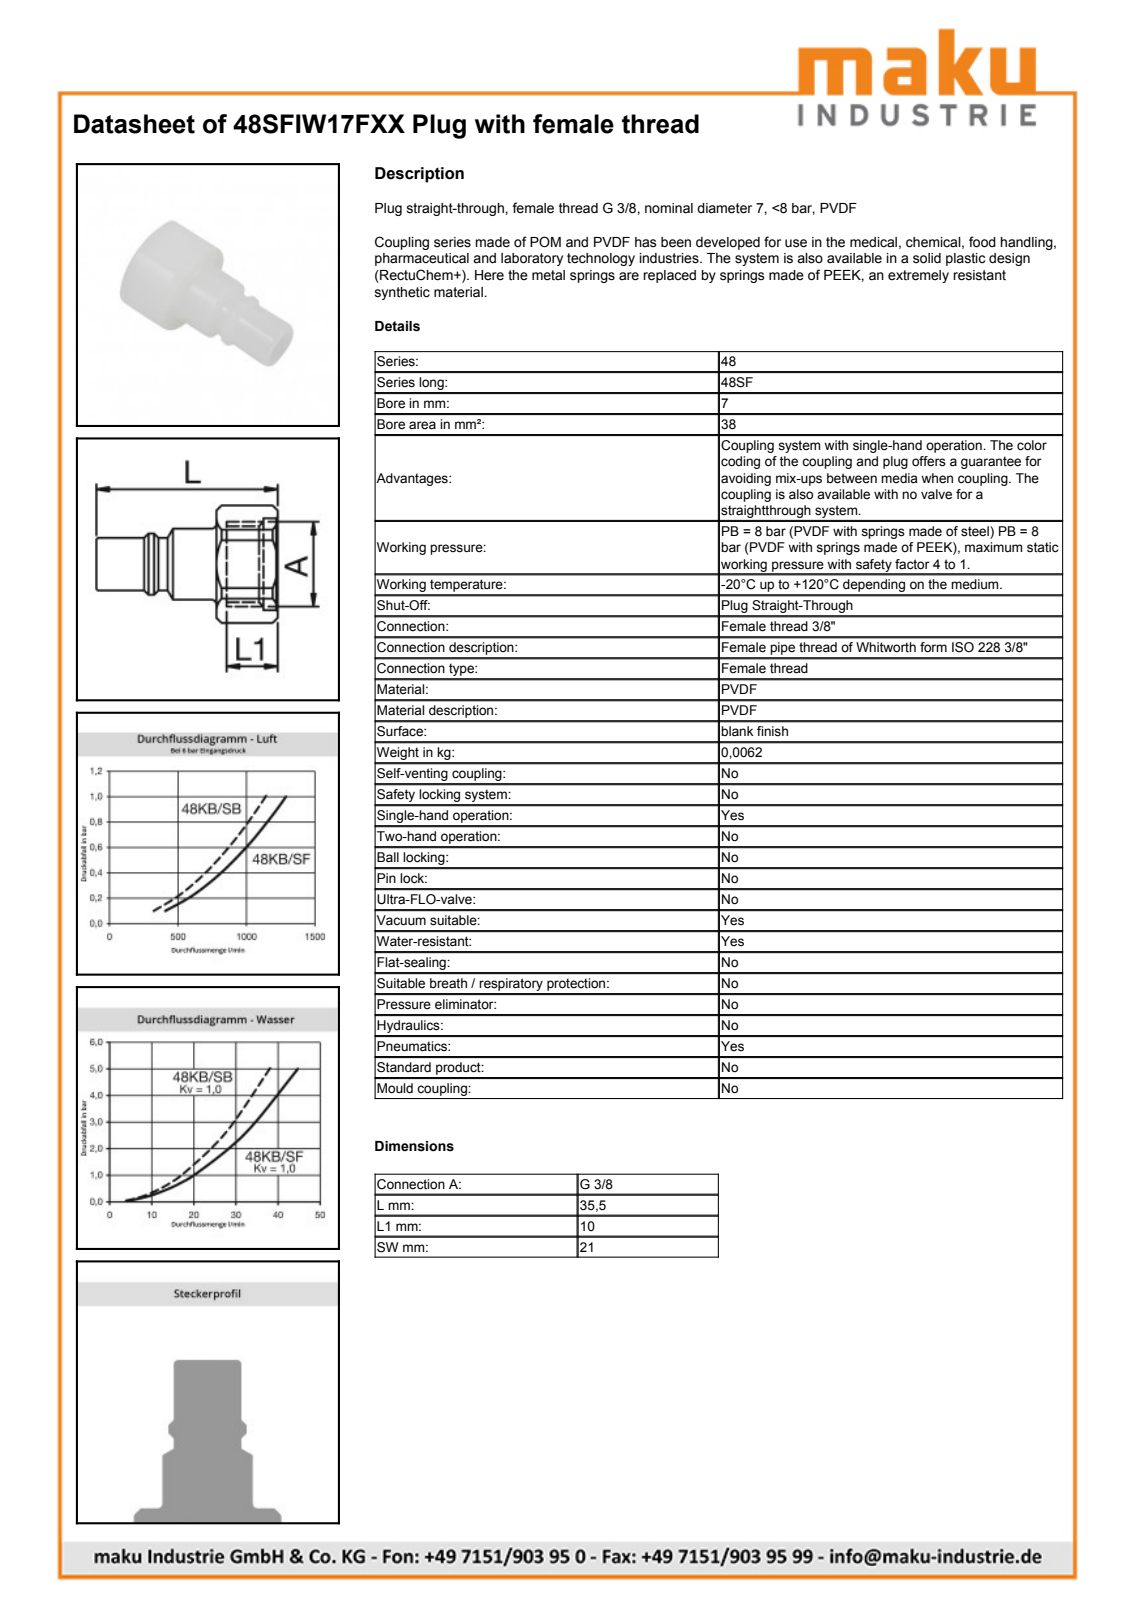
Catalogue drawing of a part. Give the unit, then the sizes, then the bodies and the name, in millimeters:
Units: millimetres
Overall size (bounding box): 35.5 × 23 × 21
Round holes (diameter × count): ⌀7 ×1, ⌀10.05 ×1, ⌀16.66 ×1, ⌀18 ×1
Round bosses / shafts (diameter × count): ⌀13.9 ×1, ⌀12 ×1, ⌀10.3 ×1
Partial cylindrical surfaces — rounded edges, fillets, slot ends (radius × count): R11.5 ×1
Main face-to-face distances: 21, 2, 12, 10, 23.5, 25.5, 35.5
Volume: 3 412 mm³ · Surface area: 3 421 mm²
Bodies: 1 solid, 36 faces (10 planar, 14 cylindrical, 12 other)
Part name (STEP PRODUCT): D104407
STEP written by: Autodesk Inventor 2011 (AUTOMOTIVE_DESIGN)
